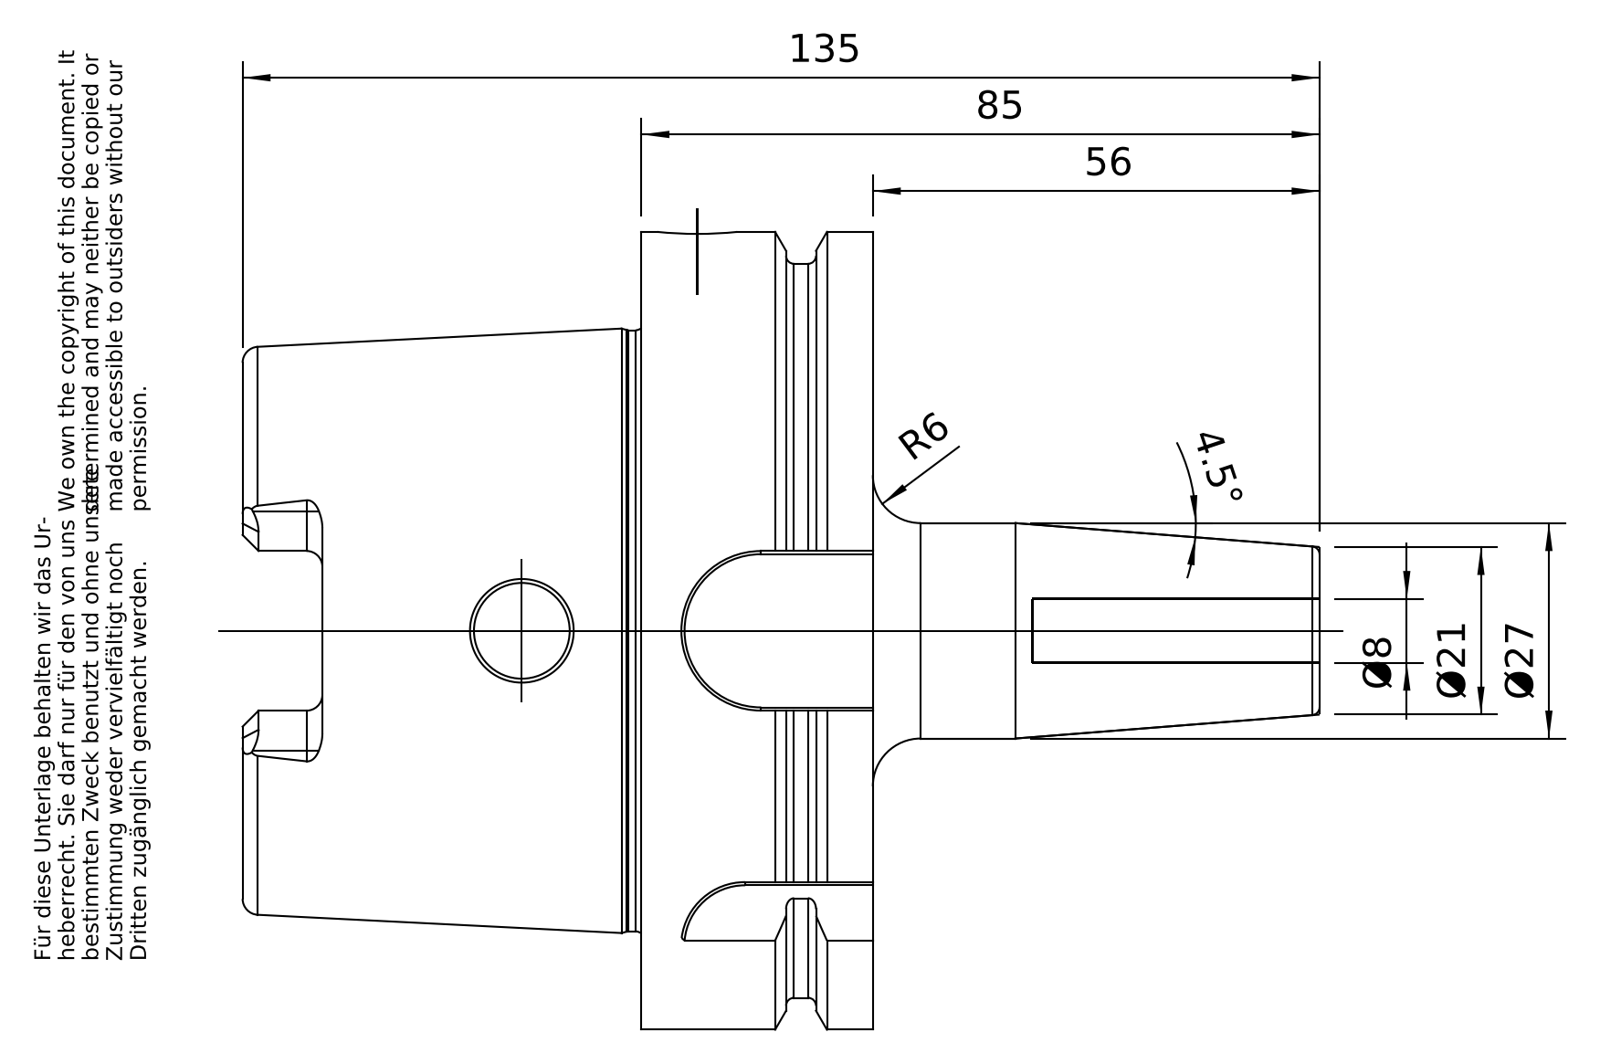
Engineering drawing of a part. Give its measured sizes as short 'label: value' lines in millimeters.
name: A100-140-08
written by: PRO/ENGINEER BY PARAMETRIC TECHNOLOGY CORPORATION, 2010430 (CONFIG_CONTROL_DESIGN)
unit: mm
bodies: 1 solid, 174 faces (50 planar, 51 cylindrical, 73 other)
size: 135 × 100 × 100
volume: 280 682 mm³; area: 55 088 mm²
holes: 1× ⌀8, 1× ⌀10, 1× ⌀12, 1× ⌀22.5, 1× ⌀24, 1× ⌀24.32, 1× ⌀24.5, 1× ⌀53, 1× ⌀63
bosses: 1× ⌀100, 1× ⌀92, 1× ⌀75.36, 1× ⌀27
rounds: 6× R2, 4× R5, 1× R8, 1× R10, 1× R11
face distances: 29, 12.5, 16.5, 50, 62.5, 79, 88, 78.5, 28.5, 16
